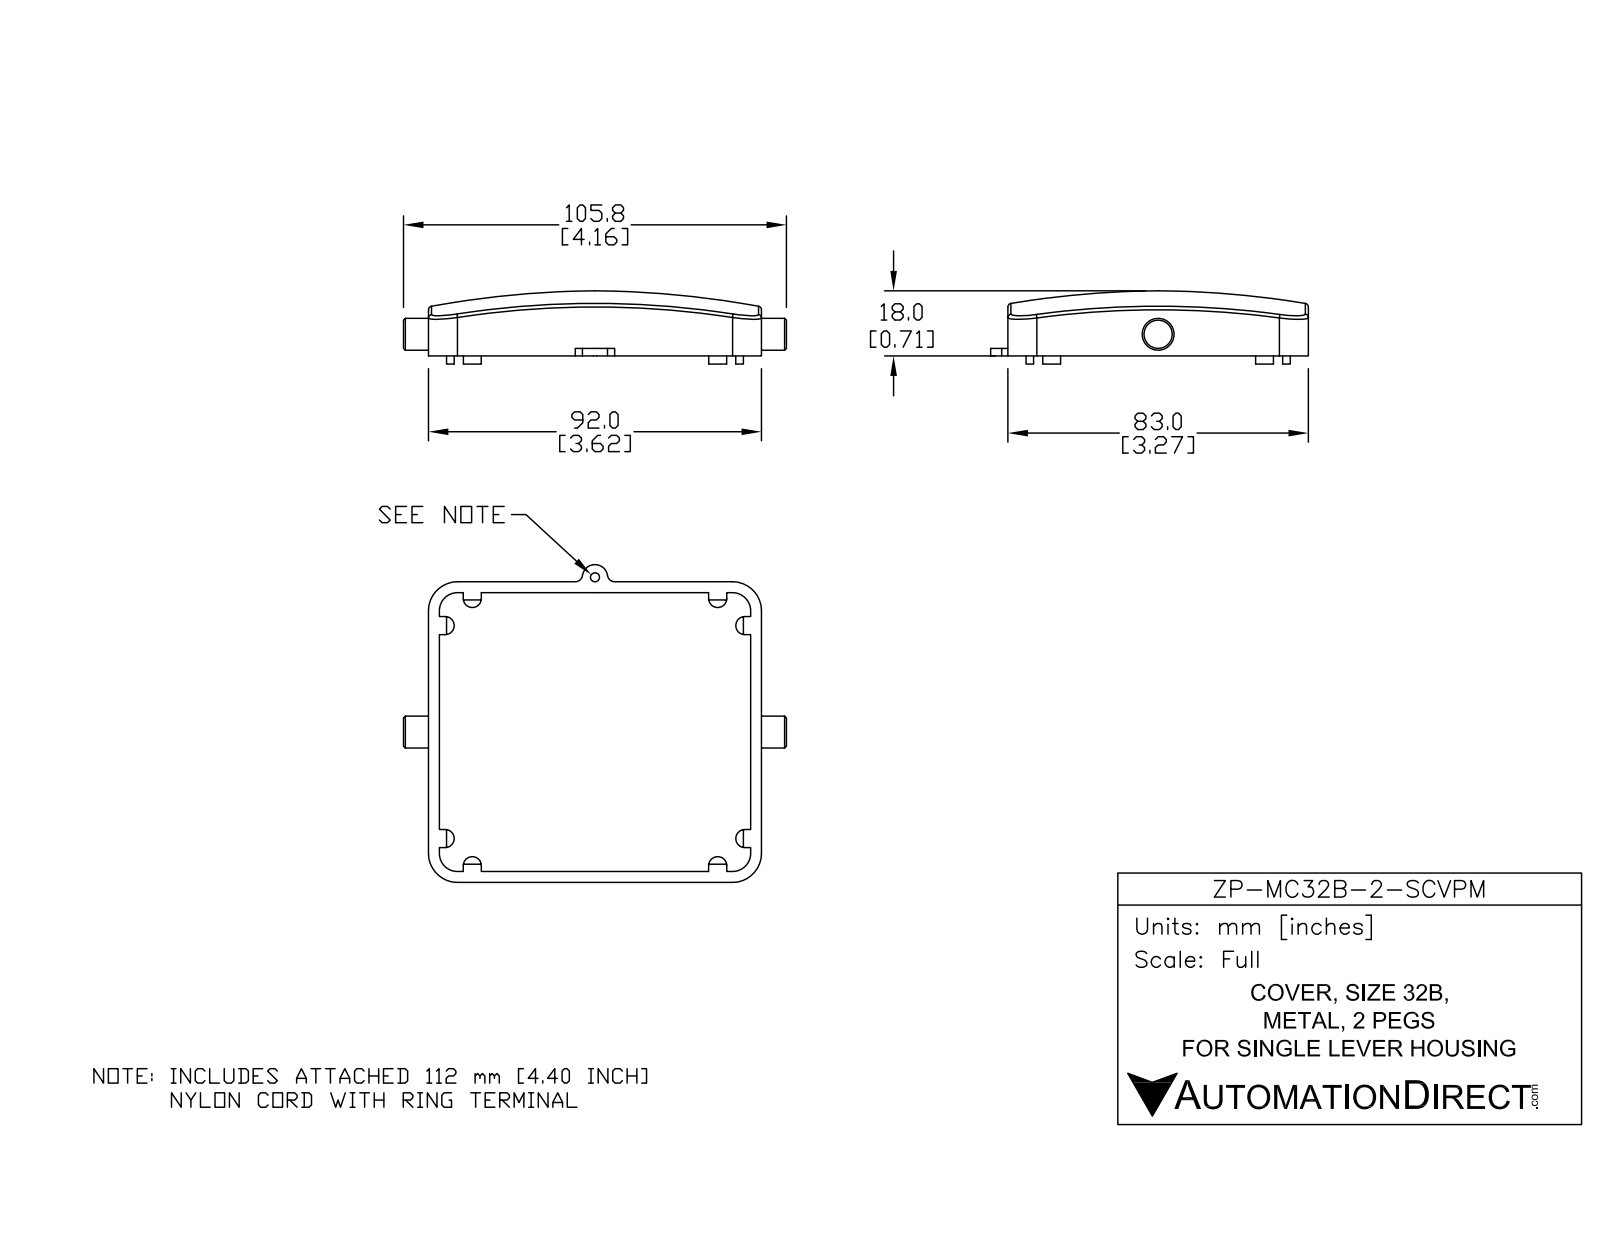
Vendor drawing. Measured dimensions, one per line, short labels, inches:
name: ZP-MC32B-2-SCVPM
written by: SolidWorks 2014 (AUTOMOTIVE_DESIGN)
unit: in
bodies: 4 solids, 129 faces (71 planar, 38 cylindrical, 20 other)
size: 7.321 × 4.165 × 2.646
volume: 2.162 in³; area: 38.76 in²
holes: 1× ⌀0.098, 1× ⌀0.161
bosses: 1× ⌀0.346
rounds: 8× R0.098, 4× R0.018, 4× R0.197, 4× R0.315, 2× R0.024, 2× R0.079, 2× R0.236, 1× R0.138
face distances: 0.118, 3.15, 3.504, 3.268, 3.622, 3.031, 3.386, 0.378, 0.197, 0.575
